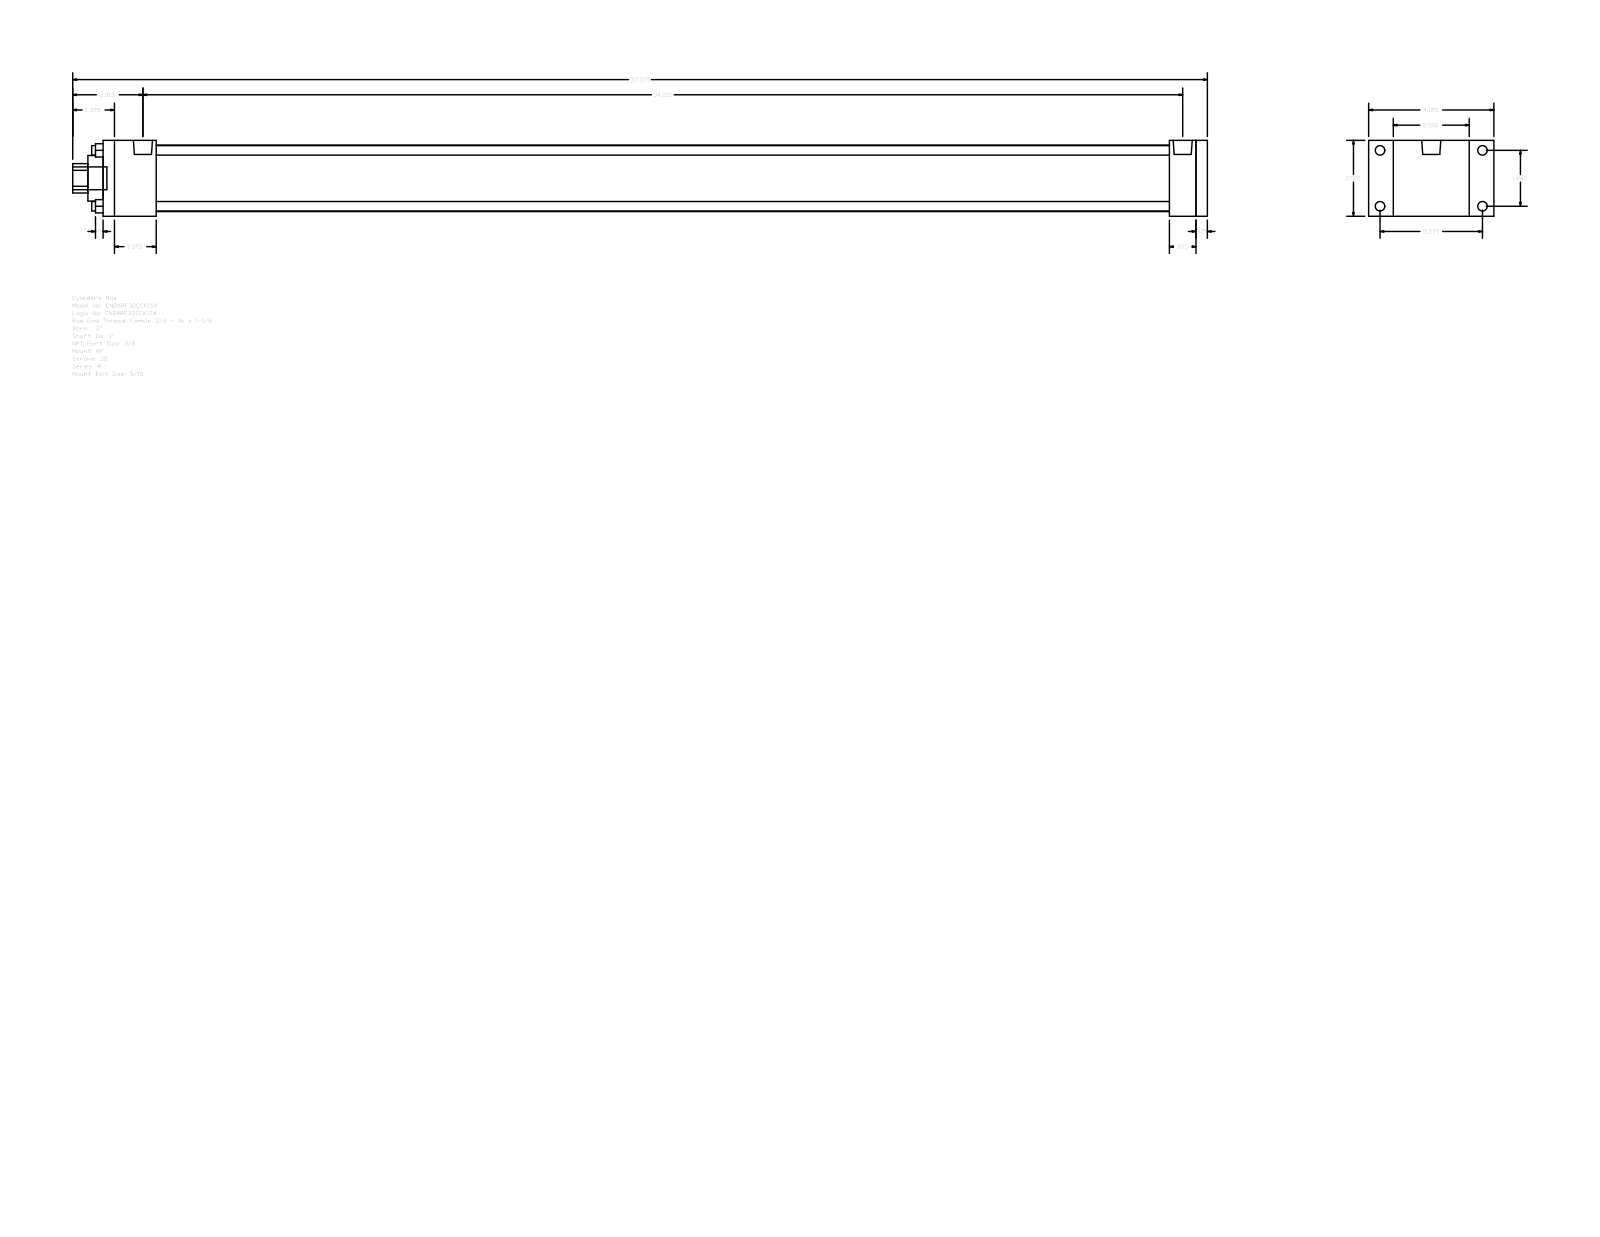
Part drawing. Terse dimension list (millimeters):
name: A_RF__0200_1
written by: GSSL Pune (CONFIG_CONTROL_DESIGN)
unit: mm
bodies: 0 solids, 92 faces (64 planar, 28 cylindrical, 0 other)
size: 949.33 × 104.78 × 63.5
holes: 4× ⌀7.94, 1× ⌀25.4, 1× ⌀38.1, 1× ⌀55.63
bosses: 4× ⌀7.94, 4× ⌀5.56, 2× ⌀15.93, 1× ⌀19.05
rounds: 1× R12.29
face distances: 63.5, 9.53, 923.93, 914.4, 20.64, 44.45, 869.95, 879.48, 892.18, 847.73
hole spacings: 33.05, 46.74, 66.1
